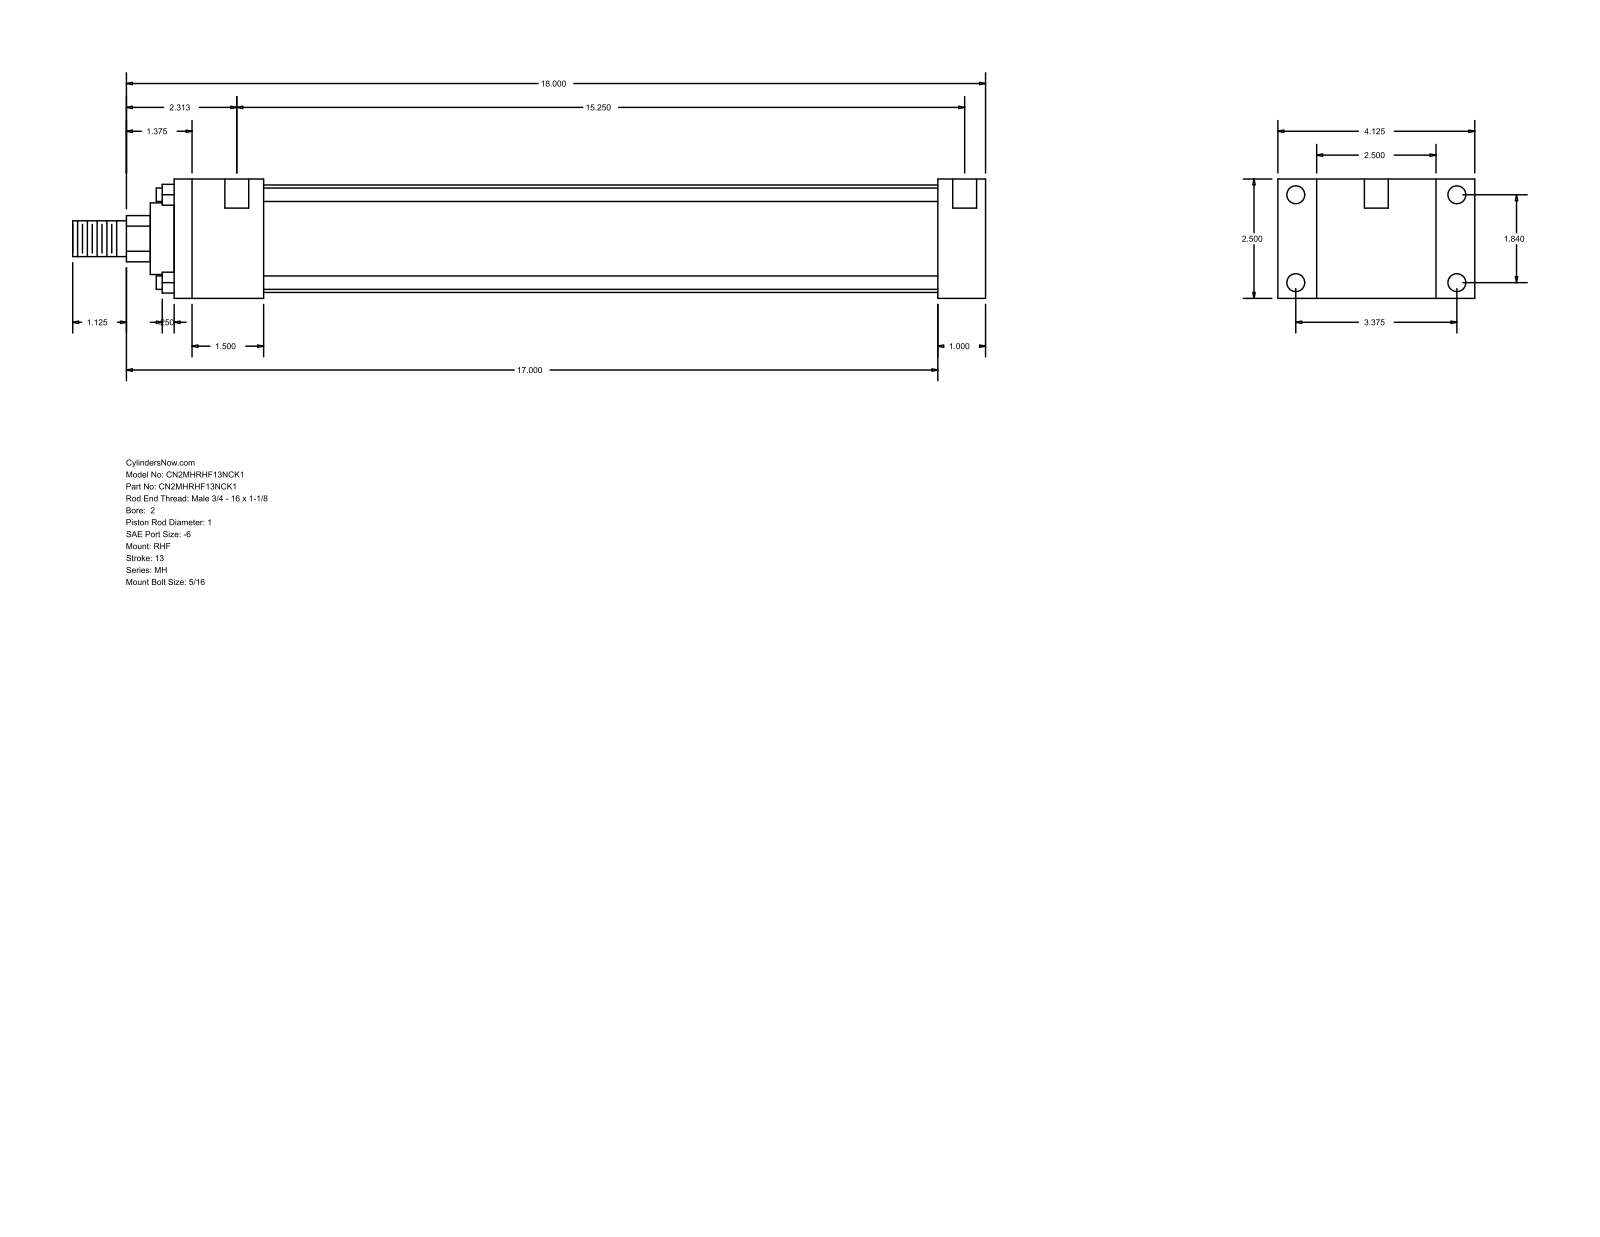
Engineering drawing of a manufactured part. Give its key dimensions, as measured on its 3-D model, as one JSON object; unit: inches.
{"part_name": "MH_RHF__0200_1", "step_written_by": "GSSL Pune (CONFIG_CONTROL_DESIGN)", "units": "inches", "bodies": {"solids": 0, "faces": 88, "planar": 60, "cylindrical": 28, "other": 0}, "overall_size": [19.125, 4.125, 2.5], "round_holes": [[0.219, 4], [0.375, 4], [0.5, 2]], "round_bosses_or_shafts": [[0.281, 4], [2.25, 1], [1.5, 1], [1, 1], [0.75, 1]], "partial_cylinders_radius": [[0.484, 1]], "face_to_face_distances": [2.5, 1, 0.813, 3.313, 17, 16, 4.125, 1.875, 14.125, 15.125], "hole_center_spacings": [1.84, 3.375, 3.844, 15.562, 0.125, 0.187, 15.25, 15.375]}
